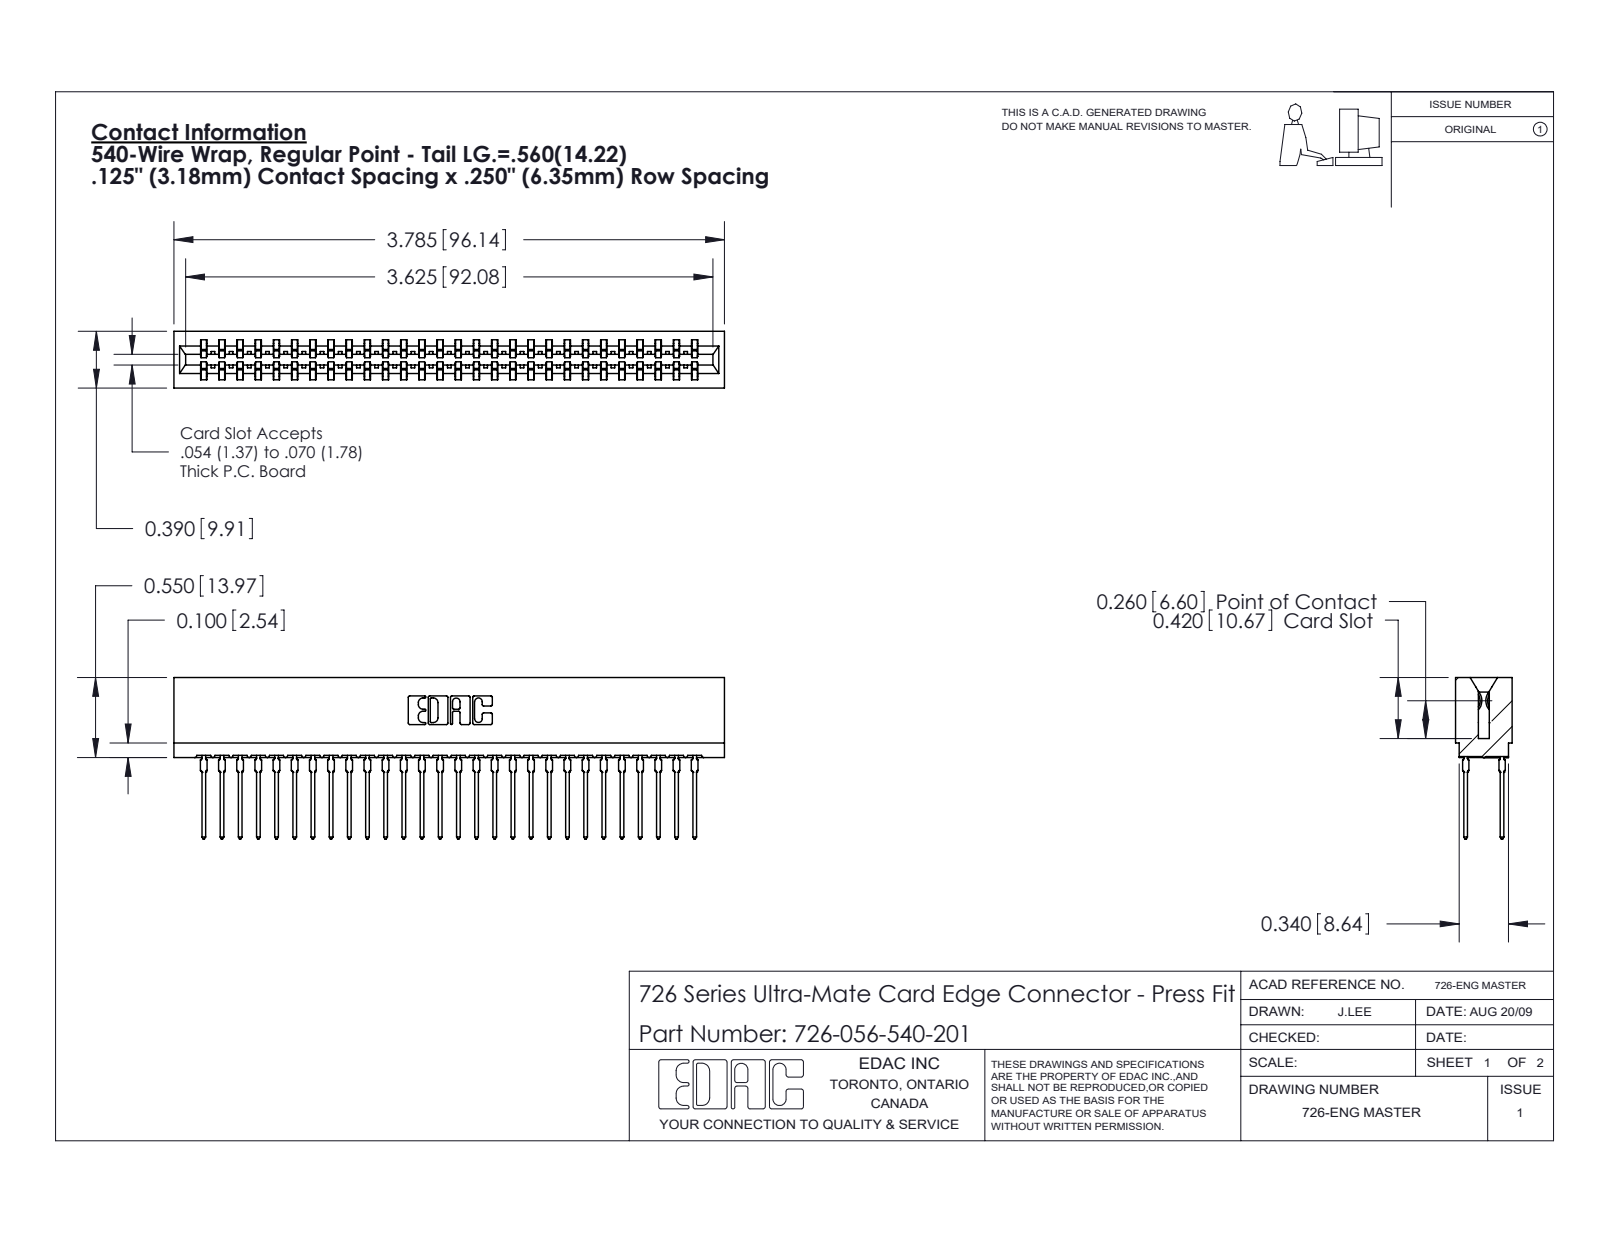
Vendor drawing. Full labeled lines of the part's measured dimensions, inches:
Part name (STEP PRODUCT): 746-292-001_540; 726 Part_.515 Slot Depth - 01; 726-056-540-201
STEP written by: SolidWorks 2020 (CONFIG_CONTROL_DESIGN)
Units: inches
Bodies: 57 solids, 5109 faces (2631 planar, 1022 cylindrical, 1456 other)
Overall size (bounding box): 3.785 × 1.109 × 0.39
Volume: 0.555 in³ · Surface area: 24.32 in²
Partial cylindrical surfaces — rounded edges, fillets, slot ends (radius × count): R0.021 ×112, R0.015 ×29, R0.01 ×22, R0.005 ×8, R0.011 ×8, R0.007 ×6, R0.031 ×6, R0.026 ×3
Main face-to-face distances: 0.057, 0.333, 0.25, 0.025, 0.307, 0.39, 0.083, 0.275, 0.5, 0.365
